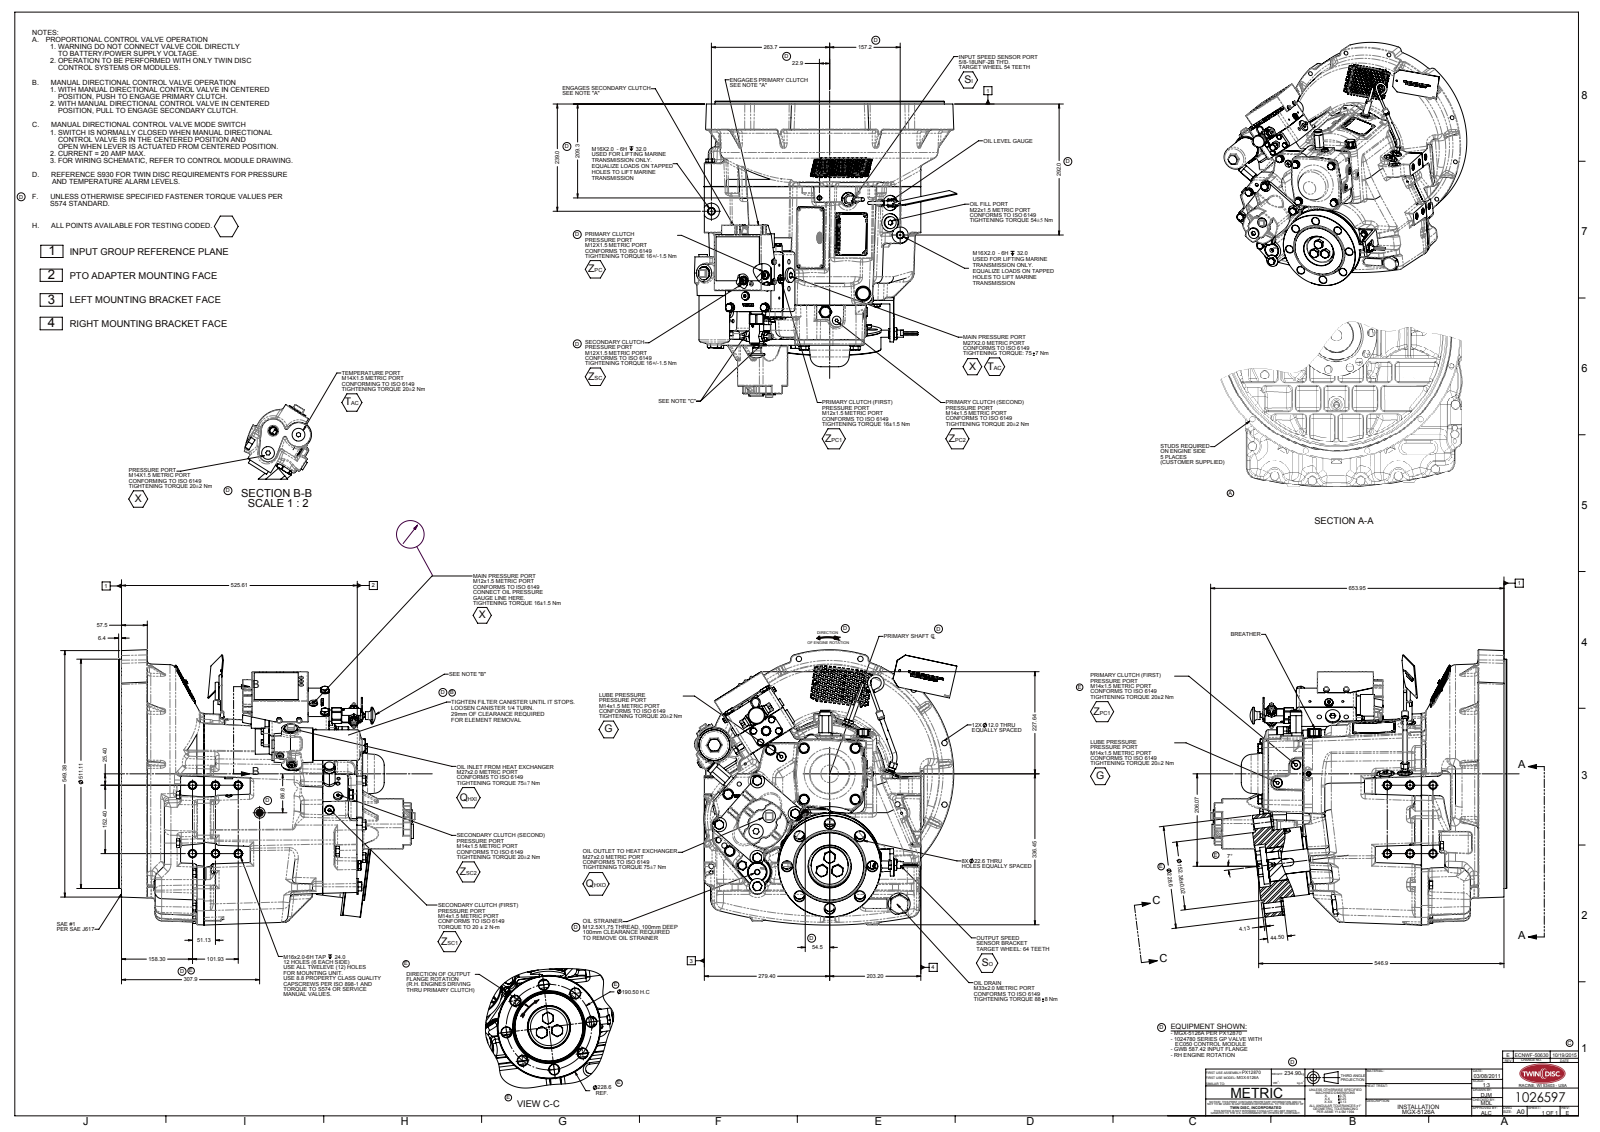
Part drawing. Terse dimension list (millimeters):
name: 1026597
written by: SolidWorks 2010 (AUTOMOTIVE_DESIGN)
unit: mm
bodies: 0 solids, 5242 faces (1371 planar, 1629 cylindrical, 2242 other)
size: 660.34 × 613.75 × 585
holes: 110× ⌀7, 14× ⌀12, 10× ⌀16.2, 8× ⌀22.62, 6× ⌀18.82, 6× ⌀23, 5× ⌀10, 4× ⌀4.8, 4× ⌀16, 4× ⌀21, 2× ⌀4.83, 2× ⌀14
bosses: 12× ⌀19.85, 10× ⌀19, 7× ⌀24, 5× ⌀17, 5× ⌀2.54, 4× ⌀20, 4× ⌀11, 3× ⌀32
rounds: 212× R8, 137× R1.5, 54× R2, 41× R3, 28× R1.02, 27× R3.5, 27× R15.1, 24× R6
face distances: 0.63, 76, 76.63, 340.48, 264.48, 263.85, 341.12, 265.12, 264.49, 0.64
hole spacings: 265.11, 20, 20.07, 26.51, 40, 34.68, 10, 30
